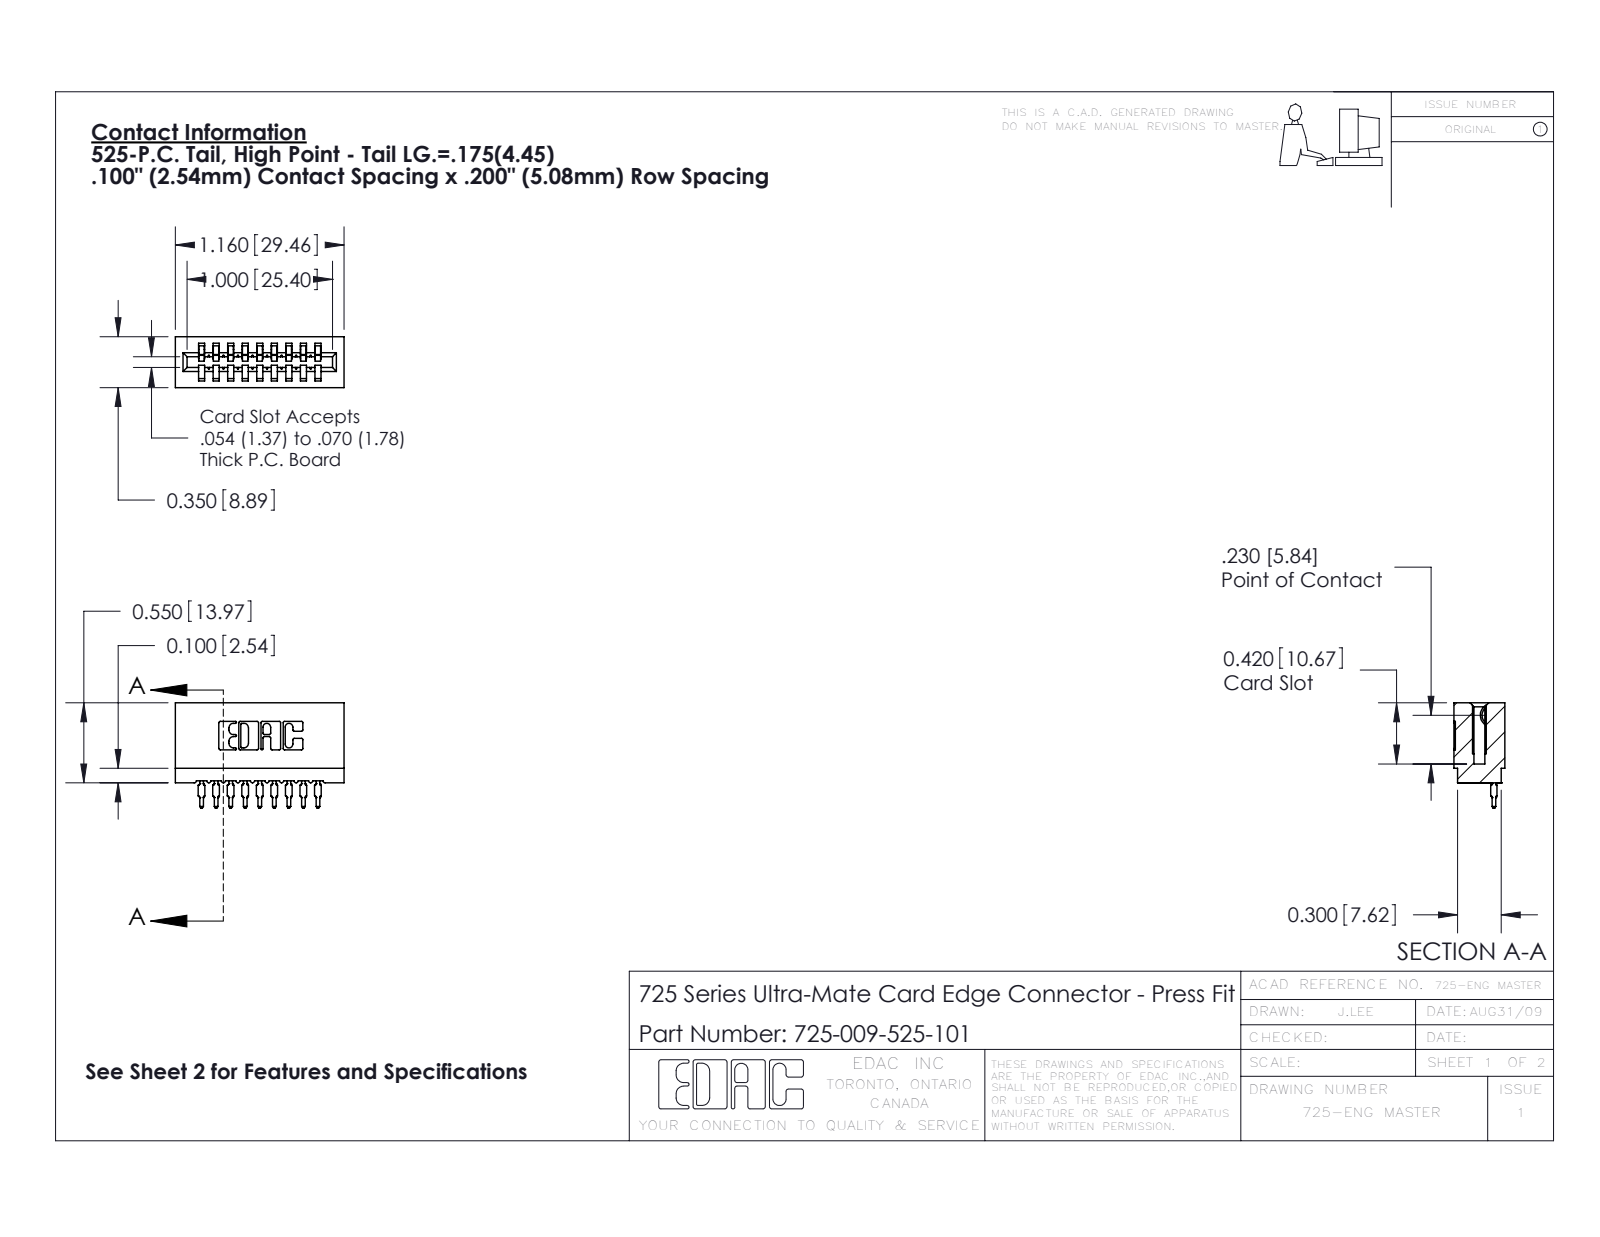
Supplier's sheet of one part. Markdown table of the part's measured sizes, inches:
| quantity | value |
| --- | --- |
| part name | 745-292-001_525; 725 Part_Insulator Option - 01; 725-009-525-101 |
| STEP written by | SolidWorks 2016 (CONFIG_CONTROL_DESIGN) |
| units | inches |
| bodies | 10 solids, 1103 faces (658 planar, 211 cylindrical, 234 other) |
| overall size | 1.16 × 0.725 × 0.35 |
| volume | 0.147 in³ |
| surface area | 6.229 in² |
| partial cylindrical surfaces (radius × count) | 0.01 × 22, 0.015 × 18, 0.021 × 18, 0.007 × 6, 0.031 × 6, 0.005 × 4, 0.011 × 4, 0.026 × 3 |
| main face-to-face distances | 0.1, 0.2, 0.3, 0.4, 0.042, 0.5, 0.142, 0.058, 0.242, 0.158 |
